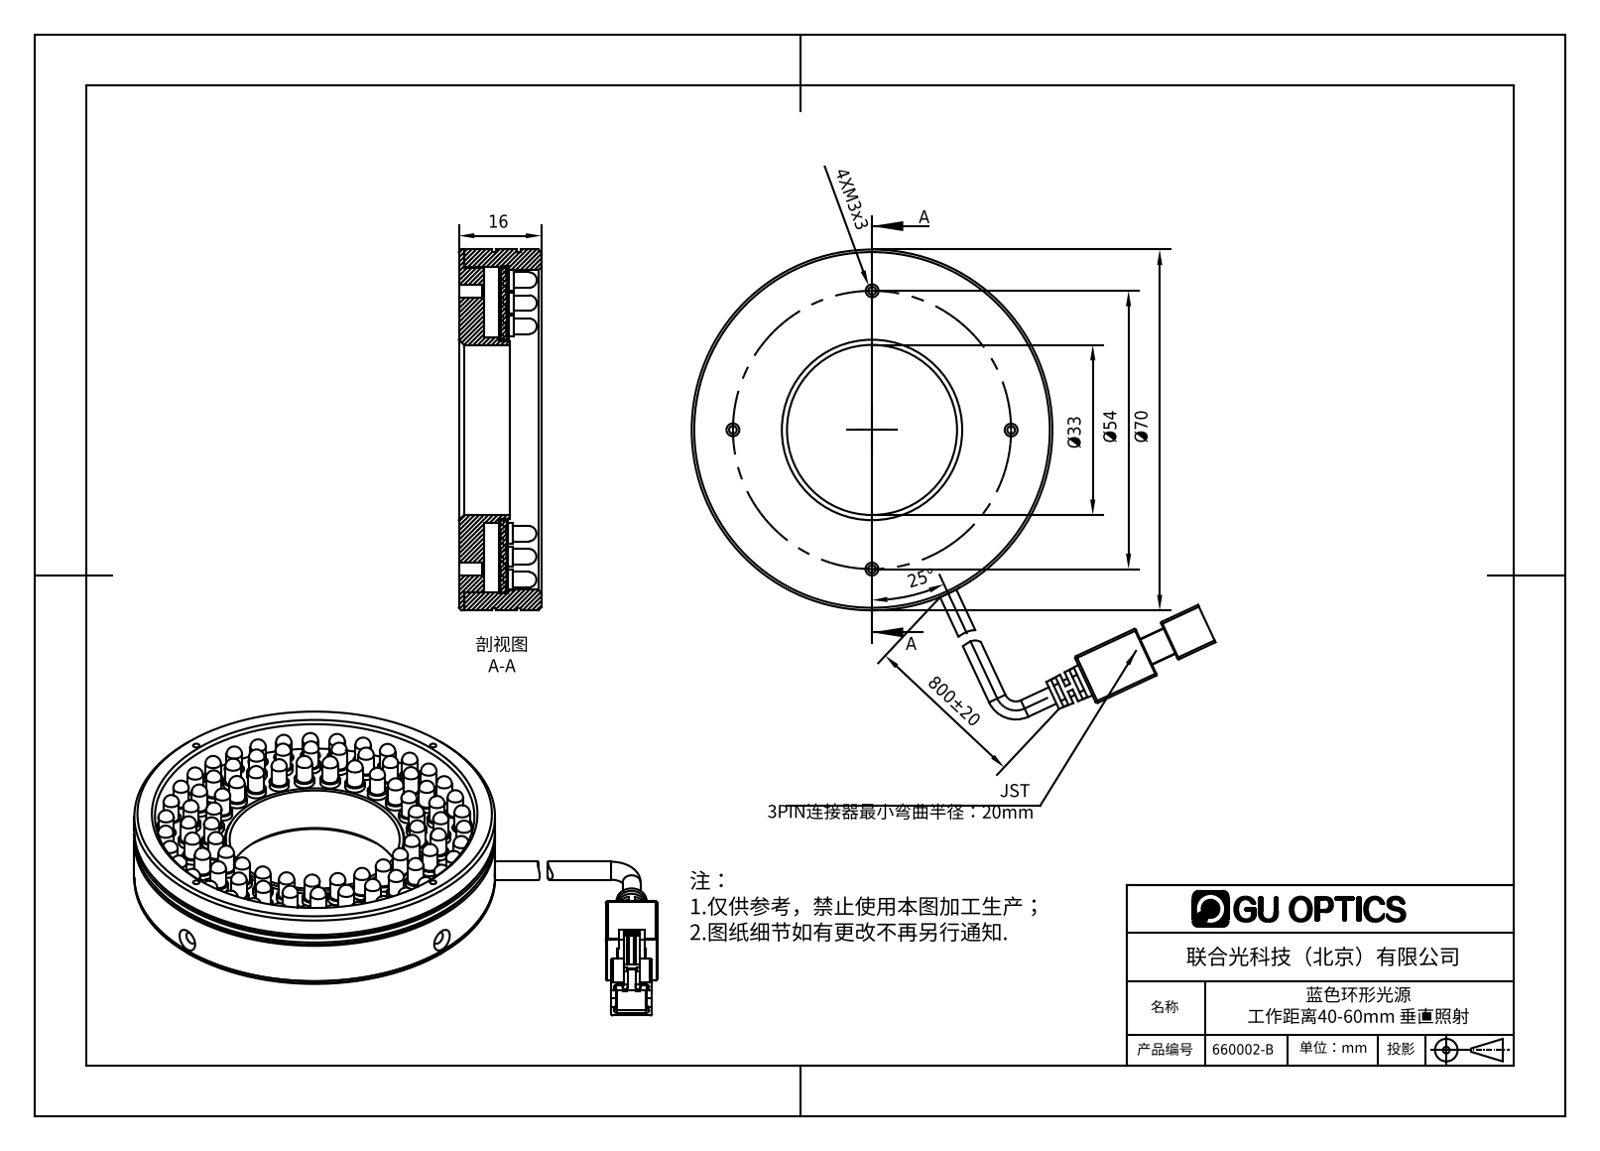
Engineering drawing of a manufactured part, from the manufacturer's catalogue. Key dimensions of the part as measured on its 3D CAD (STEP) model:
Part name (STEP PRODUCT): 660002-B
STEP written by: SolidWorks 2016 (AUTOMOTIVE_DESIGN)
Units: millimetres
Bodies: 94 solids, 1870 faces (1211 planar, 501 cylindrical, 158 other)
Overall size (bounding box): 111.72 × 78.58 × 18.5
Volume: 32 107 mm³ · Surface area: 31 402 mm²
Round holes (diameter × count): ⌀1.25 ×4, ⌀2.5 ×4, ⌀1.6 ×2, ⌀2.4 ×2, ⌀33 ×1, ⌀35 ×1, ⌀62 ×1, ⌀63.2 ×1
Round bosses / shafts (diameter × count): ⌀3.8 ×89, ⌀3 ×89, ⌀3.5 ×2, ⌀70 ×1, ⌀69 ×1, ⌀63 ×1, ⌀35.9 ×1, ⌀34.5 ×1
Partial cylindrical surfaces — rounded edges, fillets, slot ends (radius × count): R0.1 ×15, R0.2 ×13, R0.4 ×12, R0.3 ×1, R0.68 ×1, R1.4 ×1, R1.75 ×1, R7 ×1
Main face-to-face distances: 9.4, 1, 4.8, 1.6, 3, 7.8, 4.6, 8.4, 3.8, 6.8
Hole centre spacings: 26.99, 32.5, 45.96, 58.6, 11.65, 34.44, 38.17, 48.82
